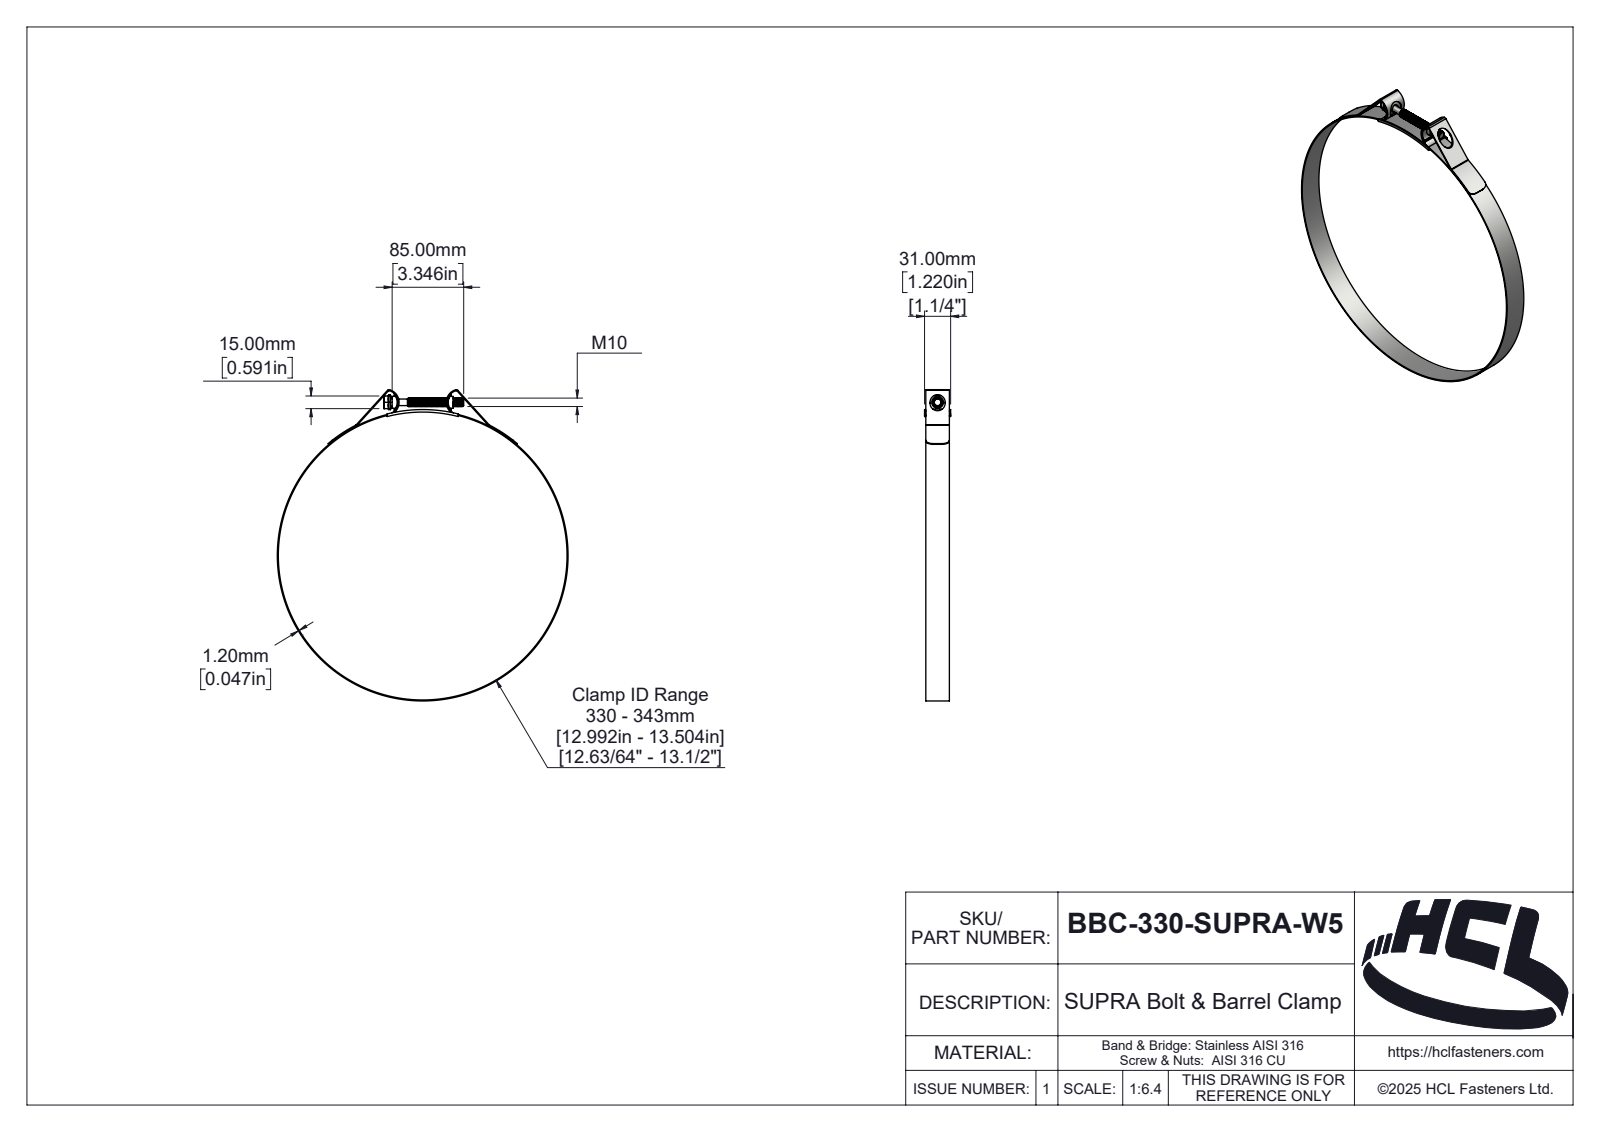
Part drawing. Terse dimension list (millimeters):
name: BBC-330-SUPRA-W5
written by: SolidWorks 2025 (AUTOMOTIVE_DESIGN)
unit: mm
bodies: 5 solids, 378 faces (50 planar, 242 cylindrical, 86 other)
size: 369.63 × 345.4 × 31
volume: 54 097 mm³; area: 86 002 mm²
holes: 1× ⌀343
bosses: 1× ⌀345.4, 1× ⌀17.32, 1× ⌀14, 1× ⌀10, 1× ⌀7.8
rounds: 4× R1, 2× R1.3, 2× R2, 2× R2.5, 2× R3.2, 2× R9, 2× R13.25, 2× R14.25
face distances: 1.2, 28, 1.5, 29.5, 29.8, 28.3, 31, 28.6, 15, 2.5
